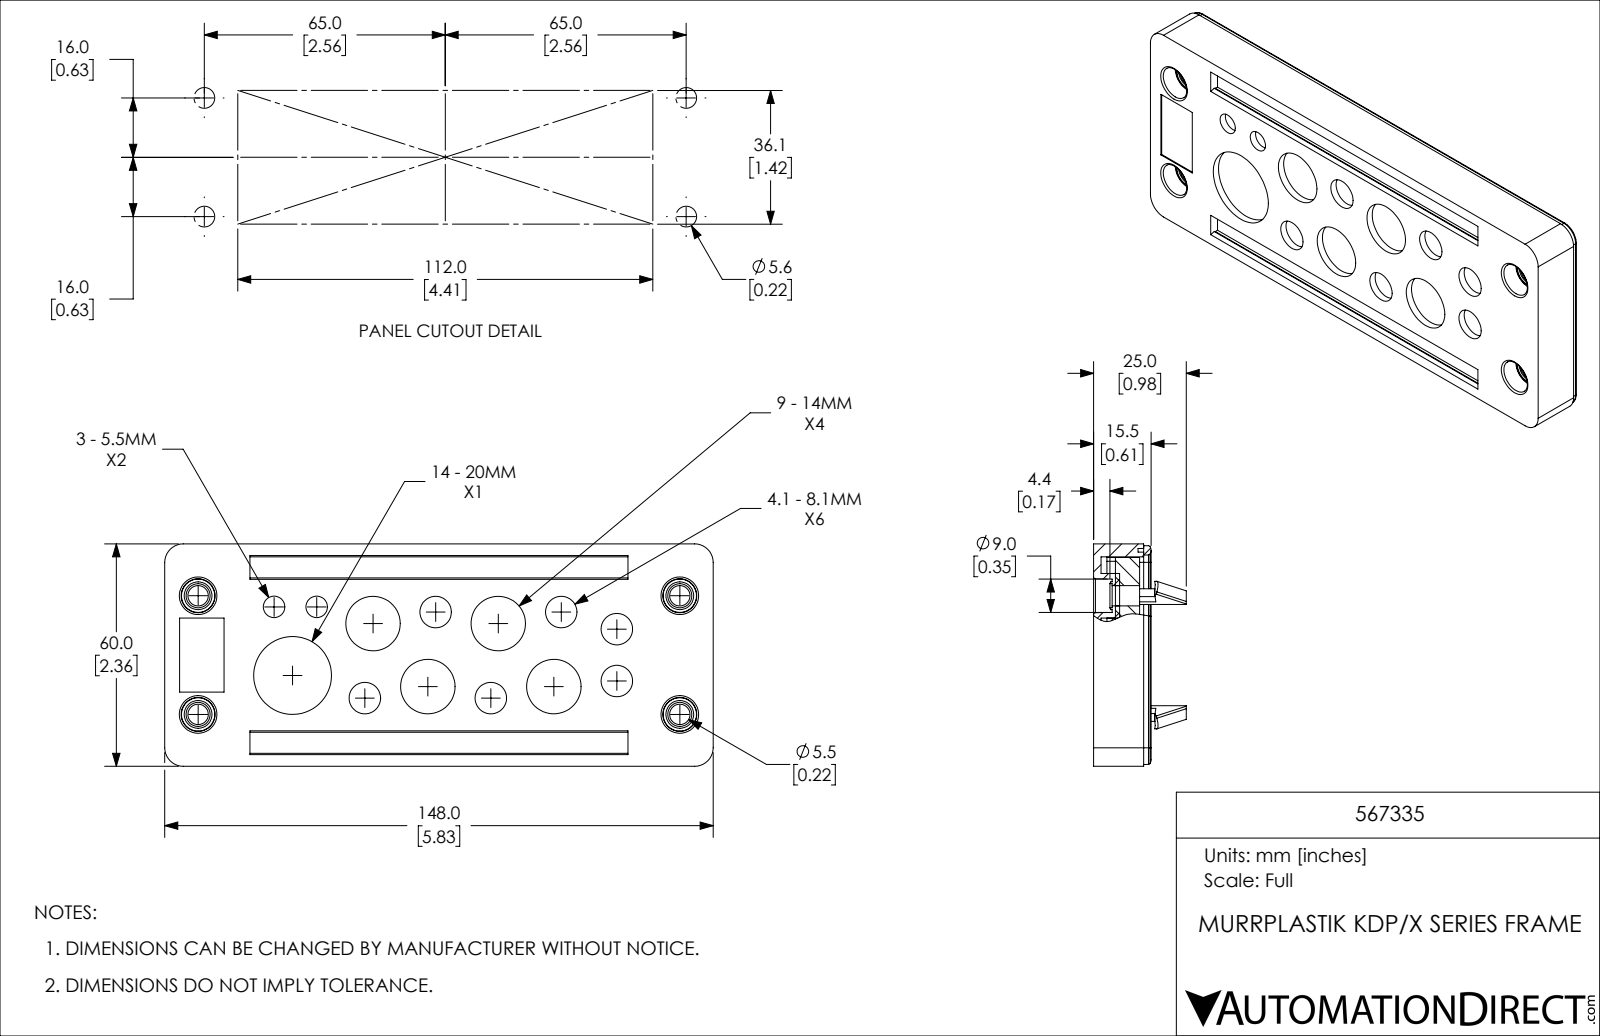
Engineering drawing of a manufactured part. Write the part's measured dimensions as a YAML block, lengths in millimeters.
part_name: "567335"
step_written_by: "SolidWorks 2019 (CONFIG_CONTROL_DESIGN)"
units: millimeters
bodies: {solids: 4, faces: 385, planar: 173, cylindrical: 176, other: 36}
overall_size: [148, 60, 25]
volume: 79115
surface_area: 63909
round_holes:
  - {diameter: 8.5, count: 6}
  - {diameter: 12.7, count: 6}
  - {diameter: 5.5, count: 4}
  - {diameter: 6.5, count: 4}
  - {diameter: 14.7, count: 4}
  - {diameter: 19, count: 4}
  - {diameter: 5.8, count: 2}
  - {diameter: 10, count: 2}
  - {diameter: 21, count: 1}
  - {diameter: 25, count: 1}
round_bosses_or_shafts:
  - {diameter: 7.5, count: 4}
partial_cylinders:
  - {radius: 2, count: 12}
  - {radius: 0.5, count: 8}
  - {radius: 1, count: 8}
  - {radius: 3, count: 8}
  - {radius: 1.5, count: 4}
  - {radius: 2.75, count: 4}
  - {radius: 3.25, count: 4}
  - {radius: 3.5, count: 4}
face_to_face_distances: [2.3, 5.9, 3.6, 6.5, 12.4, 8.8, 2, 1.6, 3.9, 10.4]
hole_center_spacings: [17.28, 17.18, 19.24, 20.2, 28.6, 32, 34, 41.23]
